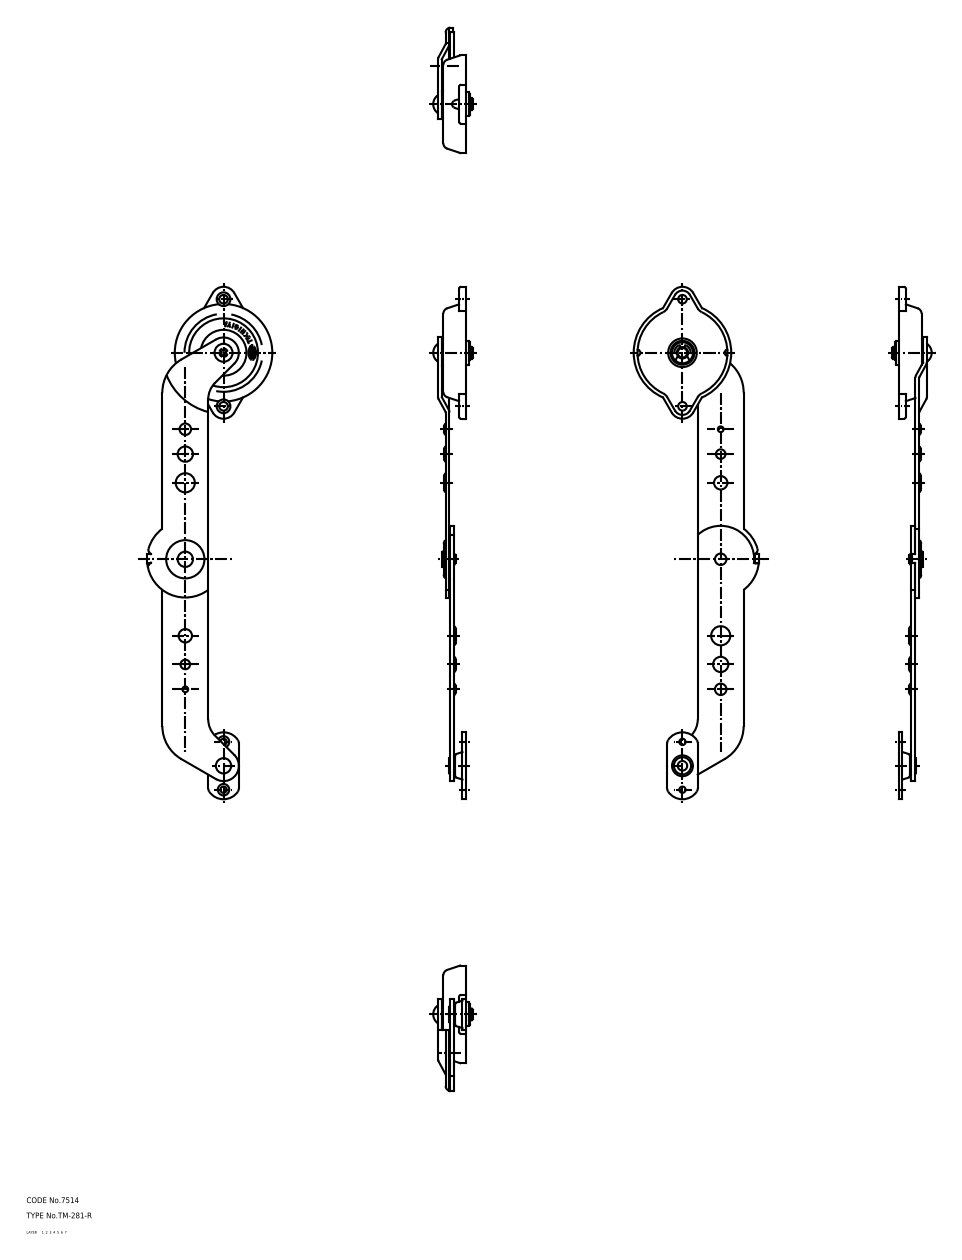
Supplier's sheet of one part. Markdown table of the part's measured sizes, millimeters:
| quantity | value |
| --- | --- |
| part name | inner ring_mr; body_mr; washer_B_mr; washer_A_mr (+8 more) |
| STEP written by | CADfix (AUTOMOTIVE_DESIGN) |
| units | millimeters |
| bodies | 14 solids, 460 faces (0 planar, 0 cylindrical, 460 other) |
| overall size | 268 × 65.5 × 20.58 |
| volume | 35 846 mm³ |
| surface area | 32 805 mm² |
